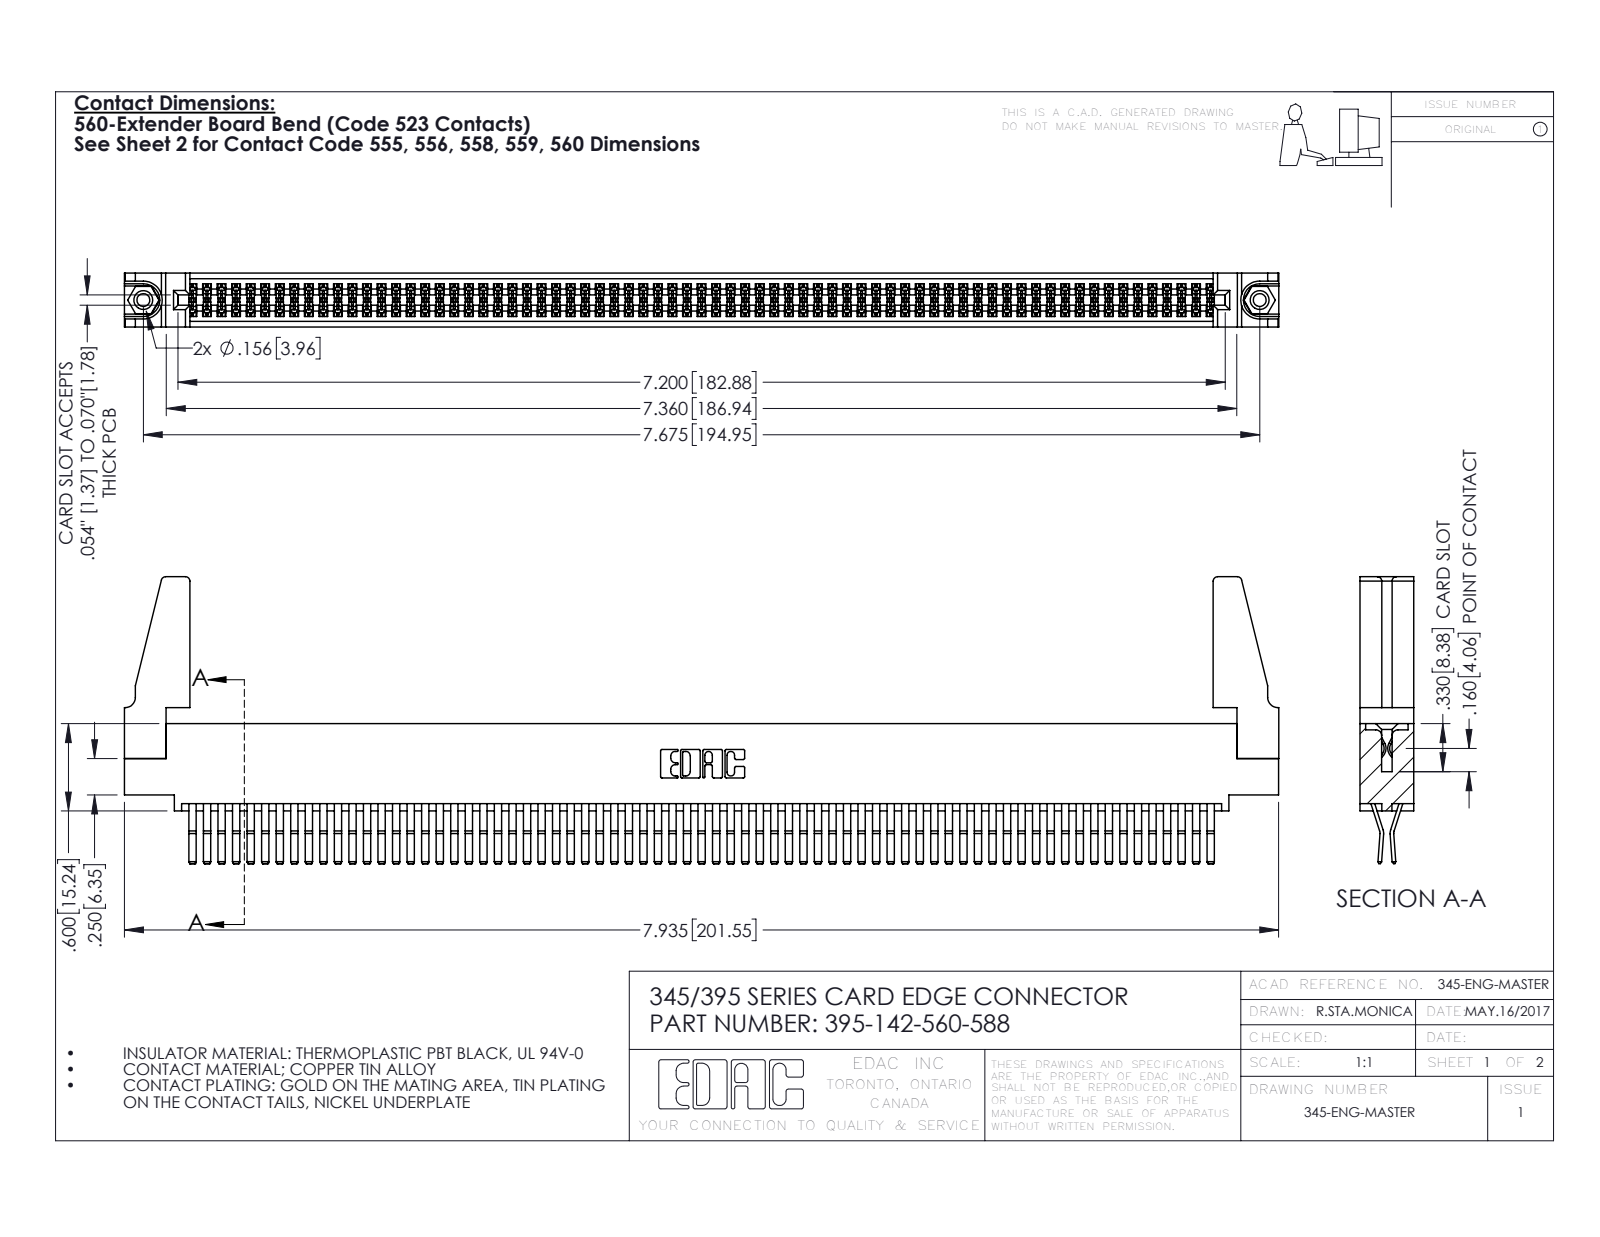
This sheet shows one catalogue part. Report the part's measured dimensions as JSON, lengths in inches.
{"part_name": "395-142-560-588; 345 Part_0.110 Offset - 0.156 Dia-TH; 345-250-001_345-250-001-102; 345-292-001_560 Tail (+1 more)", "step_written_by": "SolidWorks 2016 (CONFIG_CONTROL_DESIGN)", "units": "inches", "bodies": {"solids": 147, "faces": 7638, "planar": 4842, "cylindrical": 2780, "other": 16}, "overall_size": [7.936, 1.972, 0.37], "volume_in3": 1.462, "surface_area_in2": 57.01, "round_holes": [[0.089, 2], [0.125, 2], [0.156, 2], [0.064, 1]], "round_bosses_or_shafts": [[0.155, 2]], "partial_cylinders_radius": [[0.006, 213], [0.01, 22], [0.03, 8], [0.007, 6], [0.031, 6], [0.026, 3], [0.01, 2], [0.014, 2]], "face_to_face_distances": [0.072, 0.025, 0.298, 0.37, 0.098, 0.272, 0.2, 0.225, 0.175, 0.149], "hole_center_spacings": [0.27, 7.439, 7.675]}
